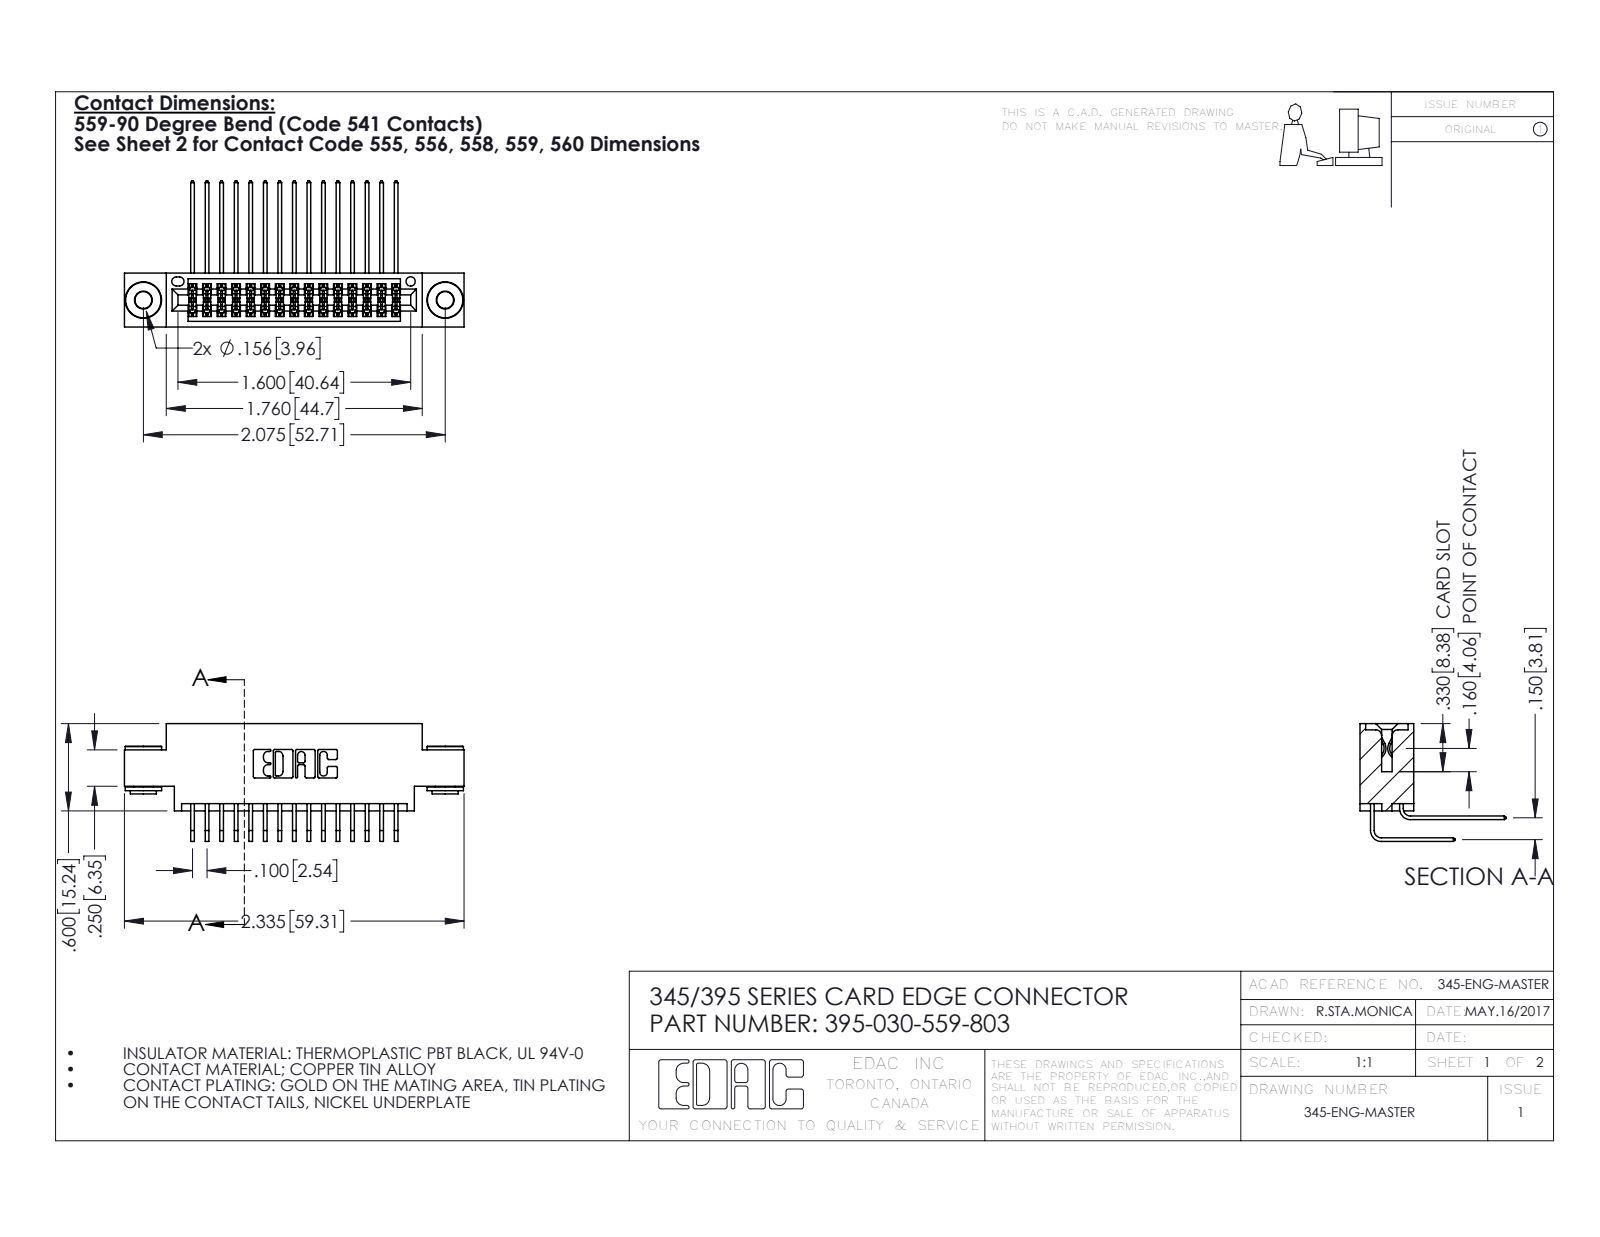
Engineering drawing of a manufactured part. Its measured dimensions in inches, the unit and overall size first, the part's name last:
Units: inches
Overall size (bounding box): 2.335 × 1.005 × 0.809
Round holes (diameter × count): ⌀0.116 ×2, ⌀0.156 ×2, ⌀0.064 ×1
Round bosses / shafts (diameter × count): ⌀0.25 ×2, ⌀0.18 ×2, ⌀0.136 ×2
Partial cylindrical surfaces — rounded edges, fillets, slot ends (radius × count): R0.006 ×45, R0.01 ×22, R0.007 ×6, R0.031 ×6, R0.026 ×3, R0.014 ×2, R0.019 ×2, R0.022 ×2
Main face-to-face distances: 0.072, 0.298, 0.37, 0.2, 0.098, 0.272, 0.025, 0.175, 0.15, 0.225
Hole centre spacings: 0.27, 1.842, 2.075
Volume: 0.341 in³ · Surface area: 13.8 in²
Bodies: 33 solids, 1728 faces (1144 planar, 576 cylindrical, 8 other)
Part name (STEP PRODUCT): 345-292-001_558 559 Tail - 1; 345-250-002_345-250-002-102; 395-030-559-803; 345-292-001_559 Tail - 2 (+1 more)
STEP written by: SolidWorks 2016 (CONFIG_CONTROL_DESIGN)
